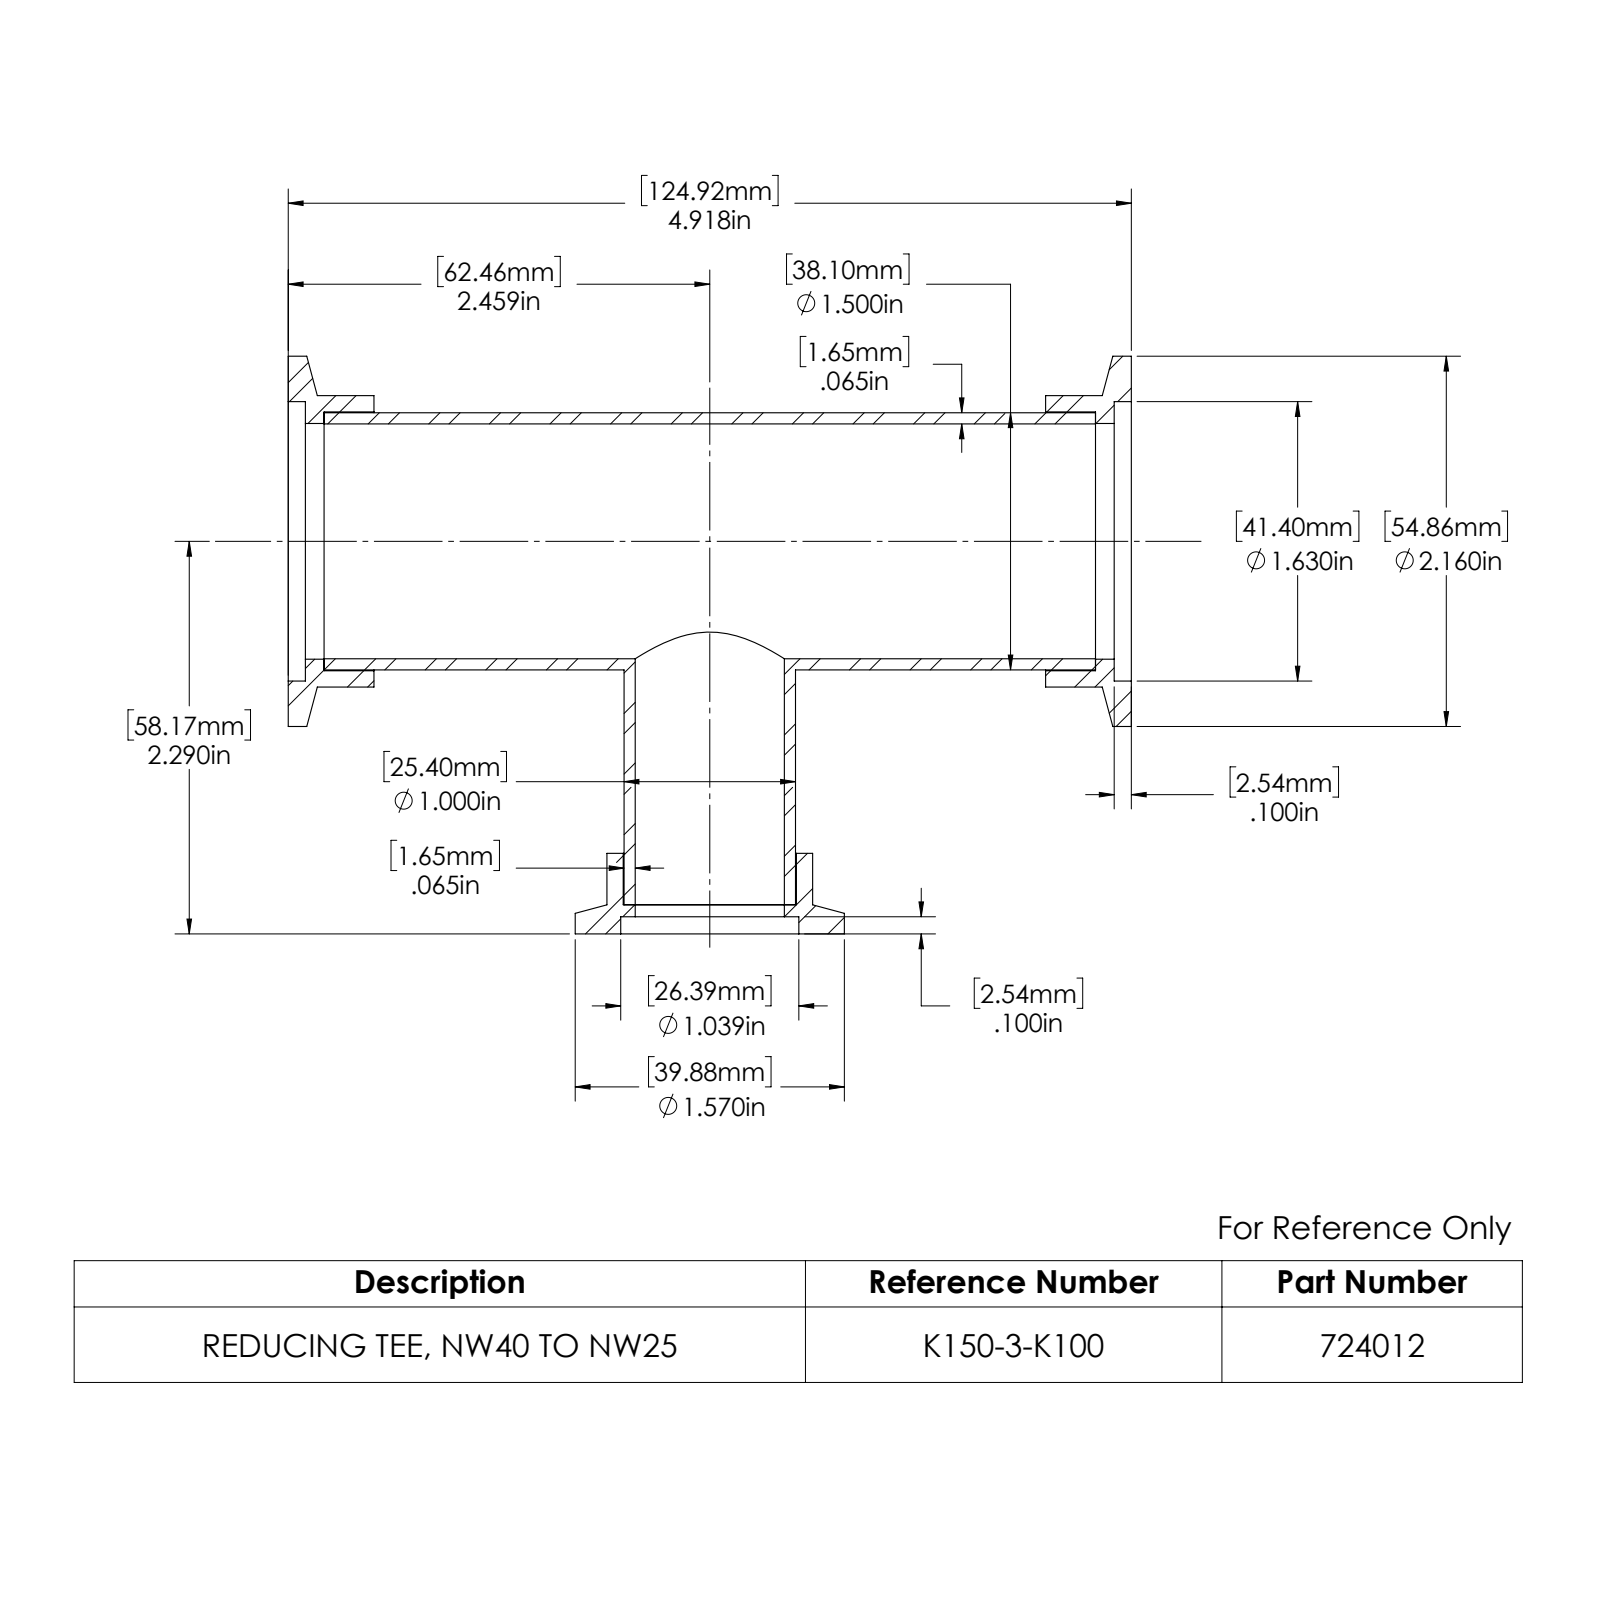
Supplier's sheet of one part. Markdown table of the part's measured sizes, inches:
| quantity | value |
| --- | --- |
| part name | 940441; 713002; 713003-99; 724012 |
| STEP written by | SolidWorks 2022 (AUTOMOTIVE_DESIGN) |
| units | inches |
| bodies | 4 solids, 59 faces (15 planar, 38 cylindrical, 6 other) |
| overall size | 4.918 × 3.37 × 2.16 |
| volume | 2.839 in³ |
| surface area | 77.25 in² |
| round holes (diameter × count) | 0.87 × 1, 1 × 1, 1.01 × 1, 1.039 × 1, 1.375 × 1, 1.5 × 1, 1.51 × 1, 1.63 × 1 |
| round bosses / shafts (diameter × count) | 2.16 × 1, 1.7 × 1, 1.57 × 1, 1.2 × 1, 1.13 × 1 |
| main face-to-face distances | 4.918, 0.1, 4.818, 0.5, 4.418, 0.4, 4.318, 0.209, 4.709, 4.5 |
